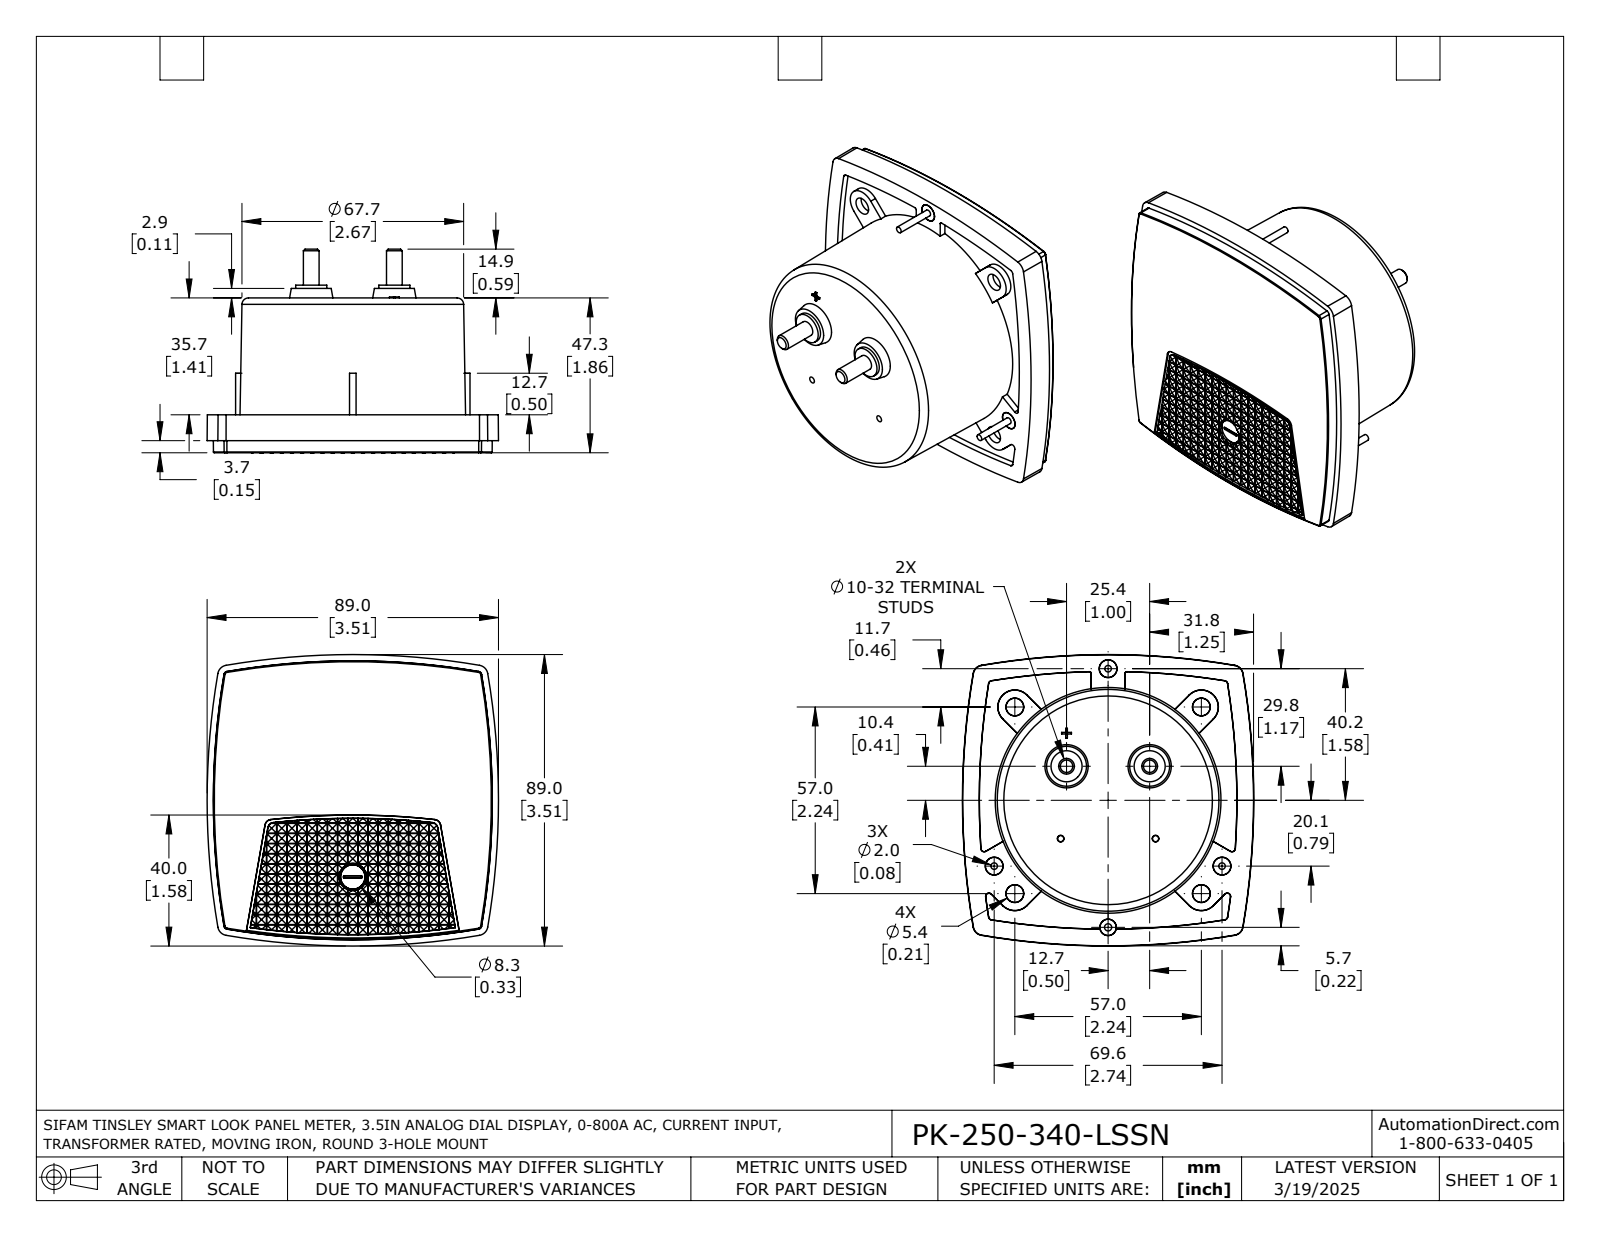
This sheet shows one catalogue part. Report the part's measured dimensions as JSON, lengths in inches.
{"part_name": "PK-250-340-LSSN", "step_written_by": "SolidWorks 2021 (AUTOMOTIVE_DESIGN)", "units": "inches", "bodies": {"solids": 1, "faces": 1078, "planar": 950, "cylindrical": 23, "other": 105}, "overall_size": [3.505, 3.505, 2.453], "volume_in3": 12.99, "surface_area_in2": 44.29, "round_holes": [[0.087, 1]], "round_bosses_or_shafts": [[0.213, 3], [0.079, 3], [0.374, 2], [0.189, 2]], "partial_cylinders_radius": [[8.961, 1]], "face_to_face_distances": [1.862, 1.406, 0.457, 0.079, 1.484, 0.378, 0.024, 0.096, 0.072, 0.12]}
